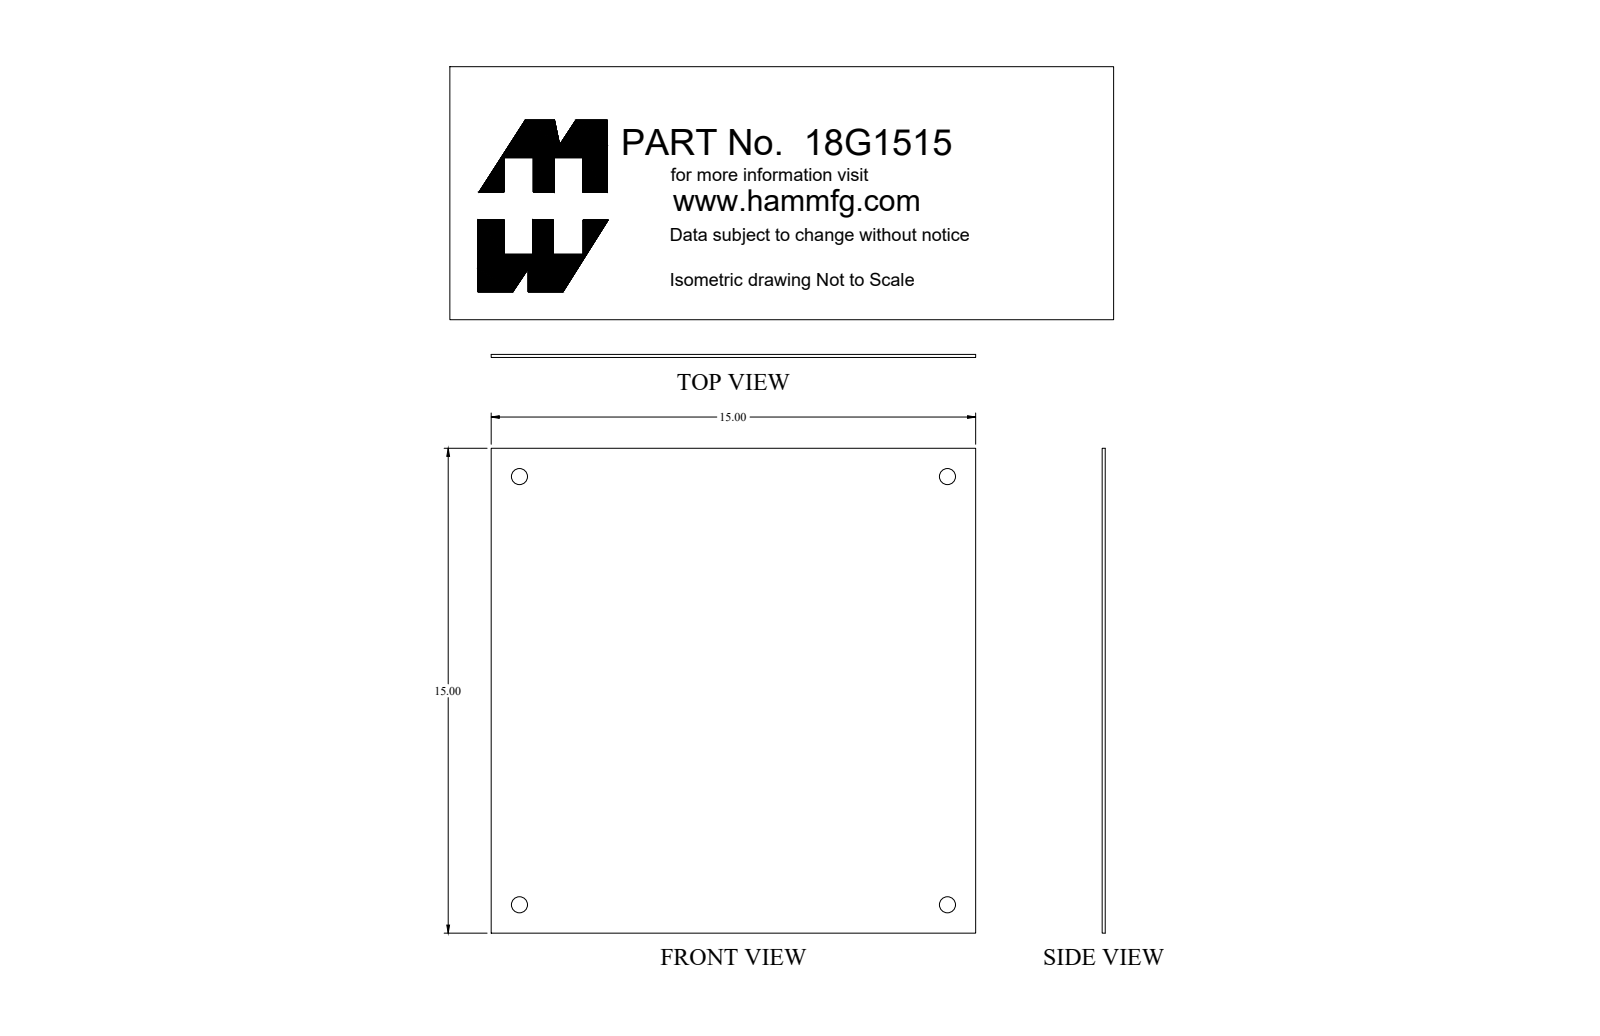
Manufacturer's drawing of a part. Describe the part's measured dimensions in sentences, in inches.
The part is named "18G1515". Its 3-D file was written by "SolidWorks 2018 (AUTOMOTIVE_DESIGN)". It is 1 solid with 10 faces: 6 planar, 4 cylindrical and 0 other. Overall it measures 15 by 15 by 0.095 inches. Its volume is 21.3 cubic inches and its surface area 454.7 square inches. Round holes: 4 of diameter 0.5. The main face-to-face distances are 0.095, 15. The hole center spacings are 13.25, 18.738.
